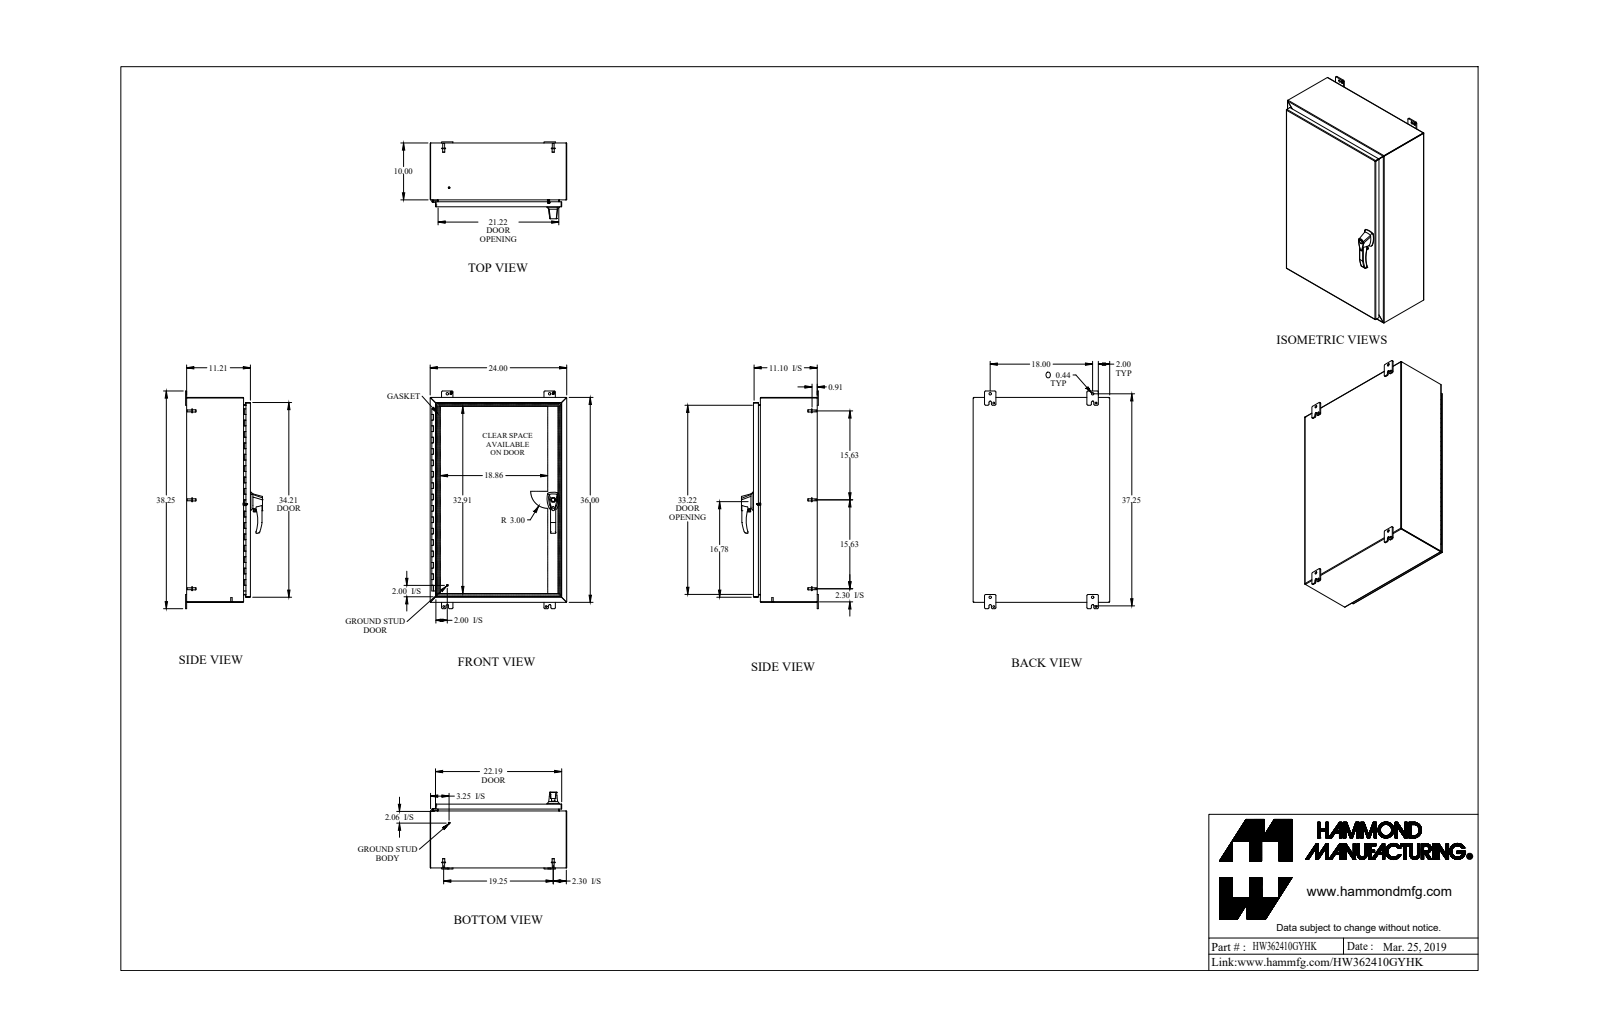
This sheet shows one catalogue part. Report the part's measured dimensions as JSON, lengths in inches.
{"part_name": "HW362410GYHK", "step_written_by": "SolidWorks 2018 (AUTOMOTIVE_DESIGN)", "units": "inches", "bodies": {"solids": 43, "faces": 1547, "planar": 747, "cylindrical": 627, "other": 173}, "overall_size": [38.25, 24, 13.512], "volume_in3": 271.5, "surface_area_in2": 7079, "round_holes": [[0.176, 6], [0.25, 4], [0.313, 4], [0.196, 3], [0.265, 3], [0.413, 3], [0.256, 2], [0.394, 2], [0.437, 2], [0.187, 1], [0.233, 1], [0.334, 1]], "round_bosses_or_shafts": [[0.375, 11], [0.65, 6], [0.33, 6], [0.25, 6], [0.156, 6], [1, 3], [0.63, 2], [0.51, 2]], "partial_cylinders_radius": [[0.25, 27], [0.188, 24], [0.036, 20], [0.108, 20], [0.06, 12], [0.125, 9], [0.045, 8], [0.218, 8]], "face_to_face_distances": [0.072, 11.138, 11.066, 0.072, 11.21, 11.138, 23.928, 35.928, 23.856, 24], "hole_center_spacings": [14.118, 14.119, 28.237, 1.111, 14.119, 18, 26.316, 37.38]}
